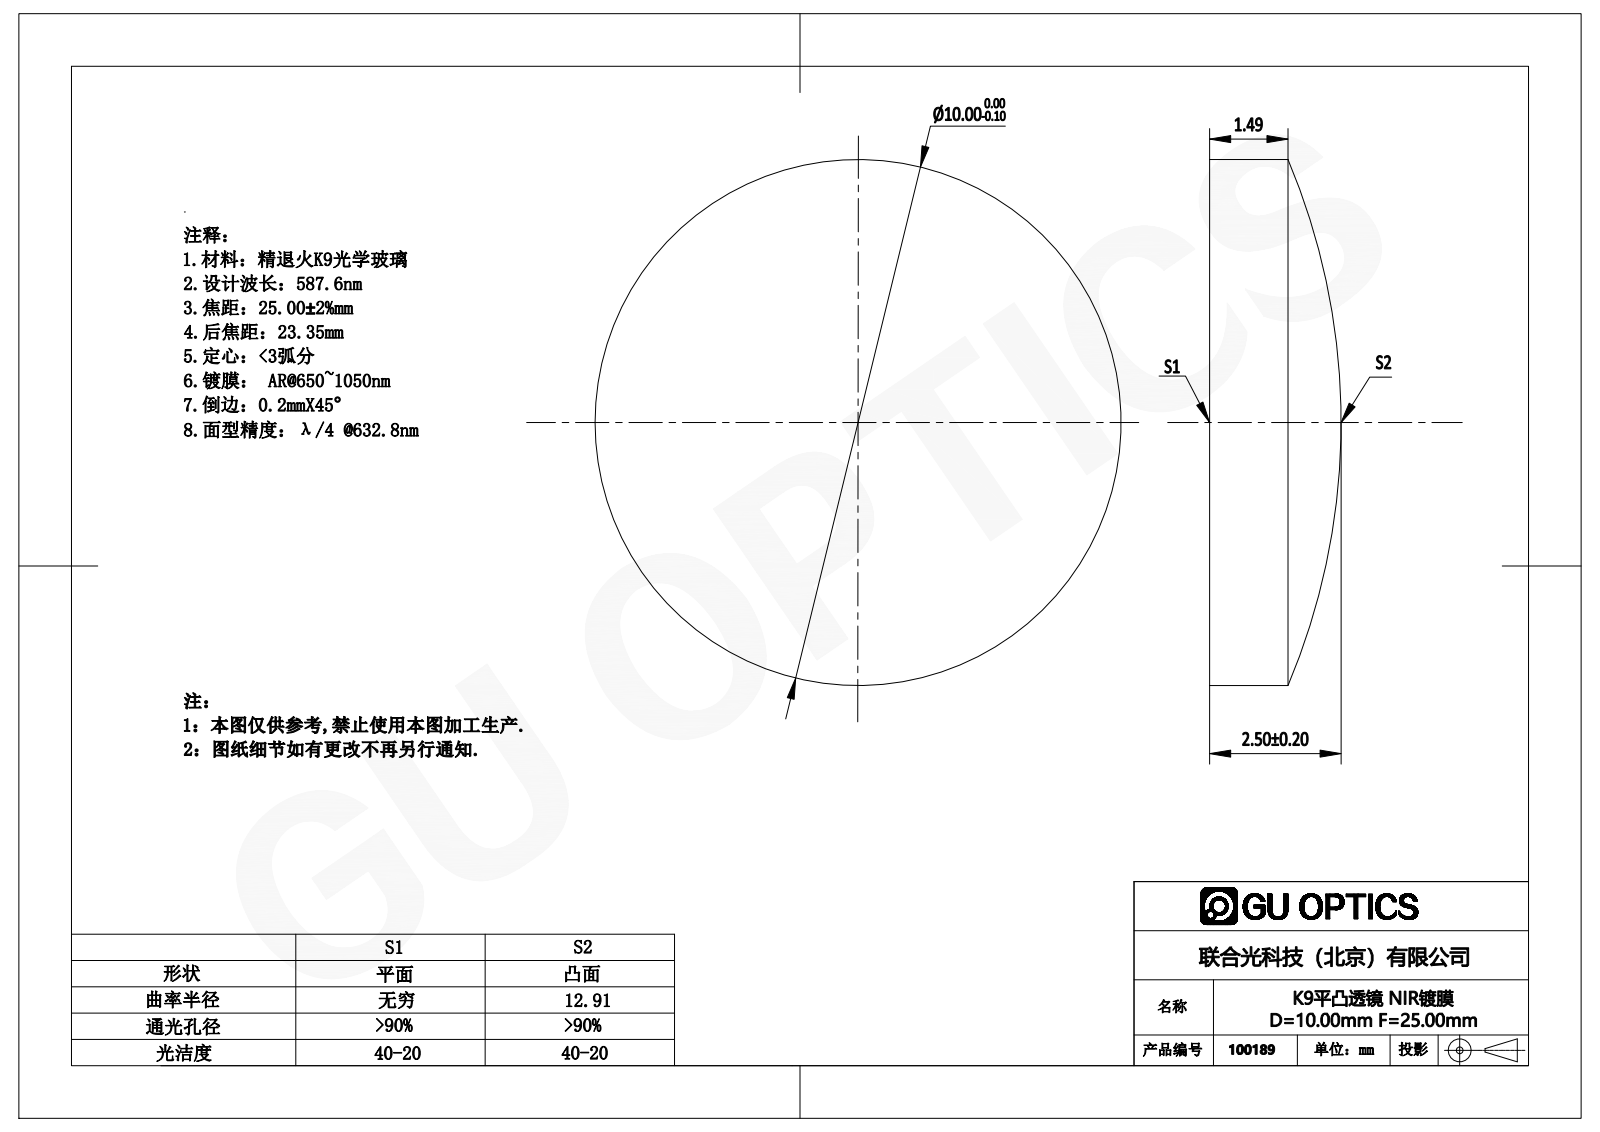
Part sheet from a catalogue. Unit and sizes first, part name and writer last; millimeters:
Units: millimetres
Overall size (bounding box): 10 × 10 × 2.5
Round bosses / shafts (diameter × count): ⌀10 ×1
Volume: 157 mm³ · Surface area: 207 mm²
Bodies: 1 solid, 5 faces (1 planar, 2 cylindrical, 2 other)
Part name (STEP PRODUCT): 100189
STEP written by: SolidWorks 2016 (AUTOMOTIVE_DESIGN)
